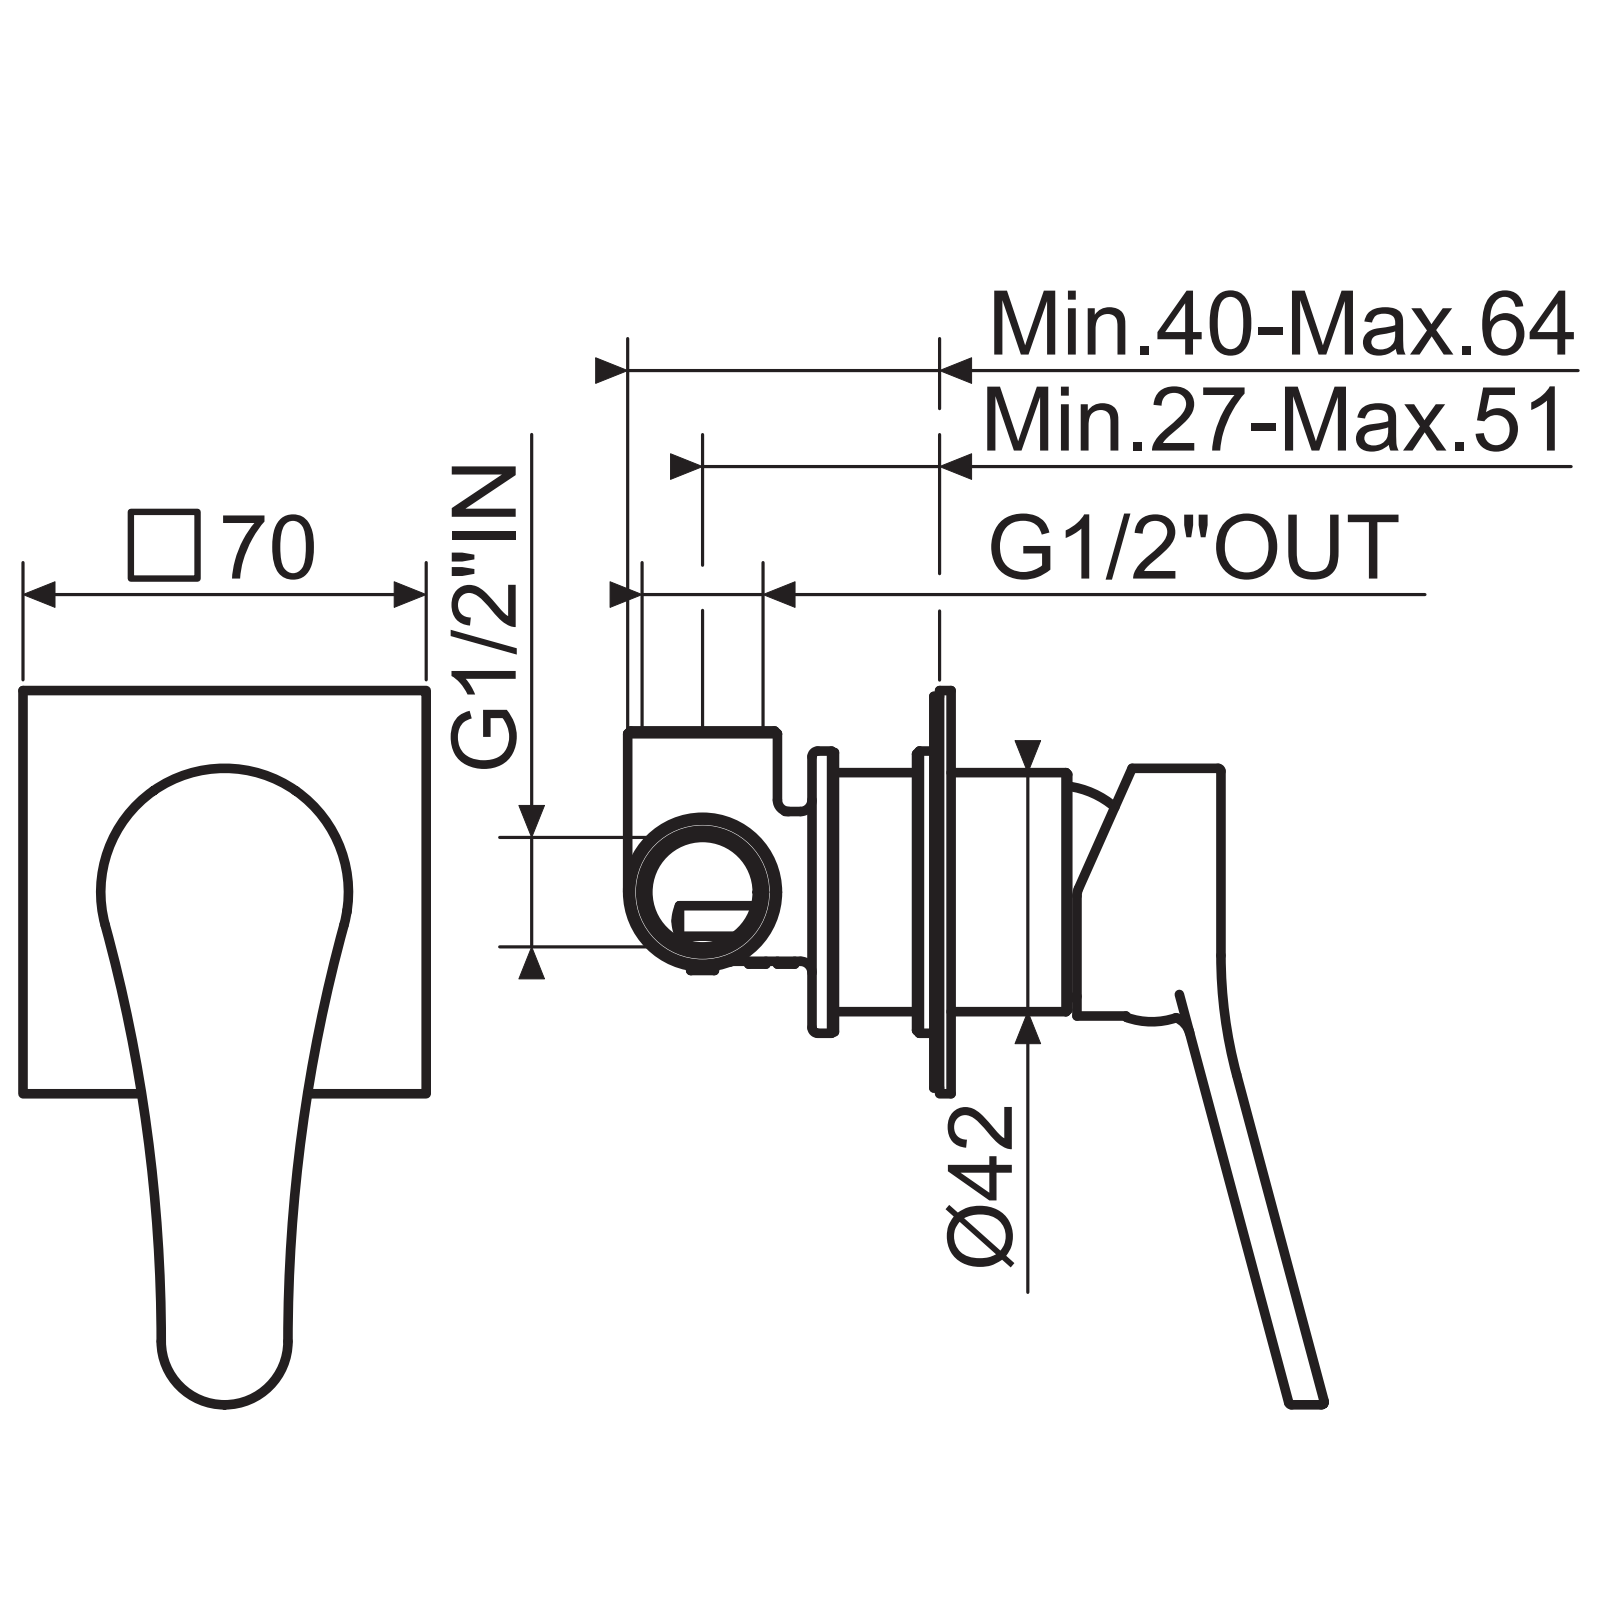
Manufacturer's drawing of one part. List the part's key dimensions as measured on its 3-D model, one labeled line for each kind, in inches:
Part name (STEP PRODUCT): SINMAC0010_AF1; AOTT230C001_AF0; AOTT608C002_AF0; AOTT230W001_AF0 (+4 more)
STEP written by: CREO PARAMETRIC BY PTC INC, 2022164 (CONFIG_CONTROL_DESIGN)
Units: inches
Bodies: 6 solids, 275 faces (62 planar, 84 cylindrical, 129 other)
Overall size (bounding box): 4.882 × 2.756 × 2.631
Volume: 1.986 in³ · Surface area: 48.91 in²
Round holes (diameter × count): ⌀0.165 ×1, ⌀0.256 ×1, ⌀0.315 ×1, ⌀1.091 ×1, ⌀1.26 ×1, ⌀1.476 ×1, ⌀1.575 ×1, ⌀1.693 ×1, ⌀1.831 ×1
Round bosses / shafts (diameter × count): ⌀1.929 ×1, ⌀1.634 ×1, ⌀1.449 ×1, ⌀0.197 ×1
Partial cylindrical surfaces — rounded edges, fillets, slot ends (radius × count): R0.02 ×23, R0.039 ×6, R0.063 ×6, R0.012 ×2, R0.059 ×2, R0.118 ×2, R10.766 ×2, R0.1 ×1
Main face-to-face distances: 0.079, 1.844, 0.236, 1.923, 1.766, 1.2, 1.556, 0.081, 1.847, 1.926
